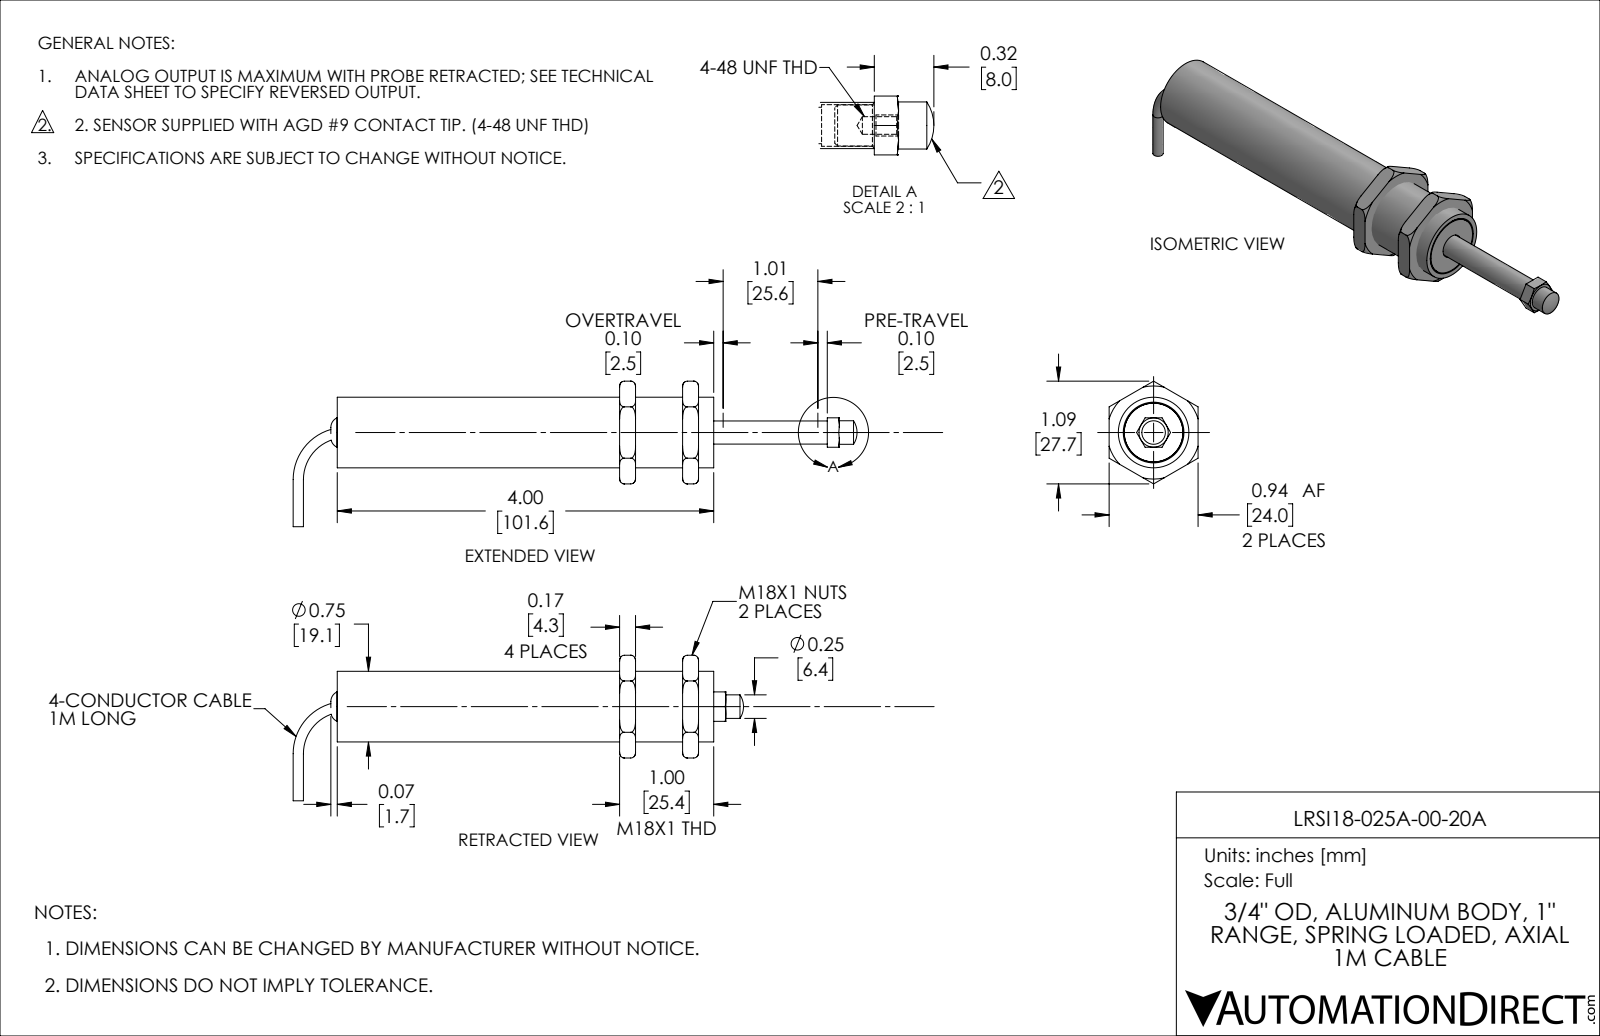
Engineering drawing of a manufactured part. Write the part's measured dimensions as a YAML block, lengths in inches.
part_name: "LRSI18-025A-00-20A"
step_written_by: "SolidWorks 2019 (AUTOMOTIVE_DESIGN)"
units: inches
bodies: {solids: 11, faces: 115, planar: 48, cylindrical: 26, other: 41}
overall_size: [4.785, 1.546, 0.945]
volume: 0.974
surface_area: 29.51
round_holes:
  - {diameter: 0.093, count: 1}
  - {diameter: 0.109, count: 1}
  - {diameter: 0.188, count: 1}
  - {diameter: 0.261, count: 1}
  - {diameter: 0.307, count: 1}
  - {diameter: 0.5, count: 1}
  - {diameter: 0.62, count: 1}
  - {diameter: 0.625, count: 1}
  - {diameter: 0.65, count: 1}
  - {diameter: 0.665, count: 1}
  - {diameter: 0.71, count: 1}
  - {diameter: 0.725, count: 1}
round_bosses_or_shafts:
  - {diameter: 0.75, count: 1}
  - {diameter: 0.7, count: 1}
  - {diameter: 0.685, count: 1}
  - {diameter: 0.624, count: 1}
  - {diameter: 0.25, count: 1}
  - {diameter: 0.218, count: 1}
  - {diameter: 0.112, count: 1}
  - {diameter: 0.109, count: 1}
face_to_face_distances: [0.669, 0.169, 0.945, 3.364, 2.364, 3.033, 1, 0.331, 2.533, 3.203]
